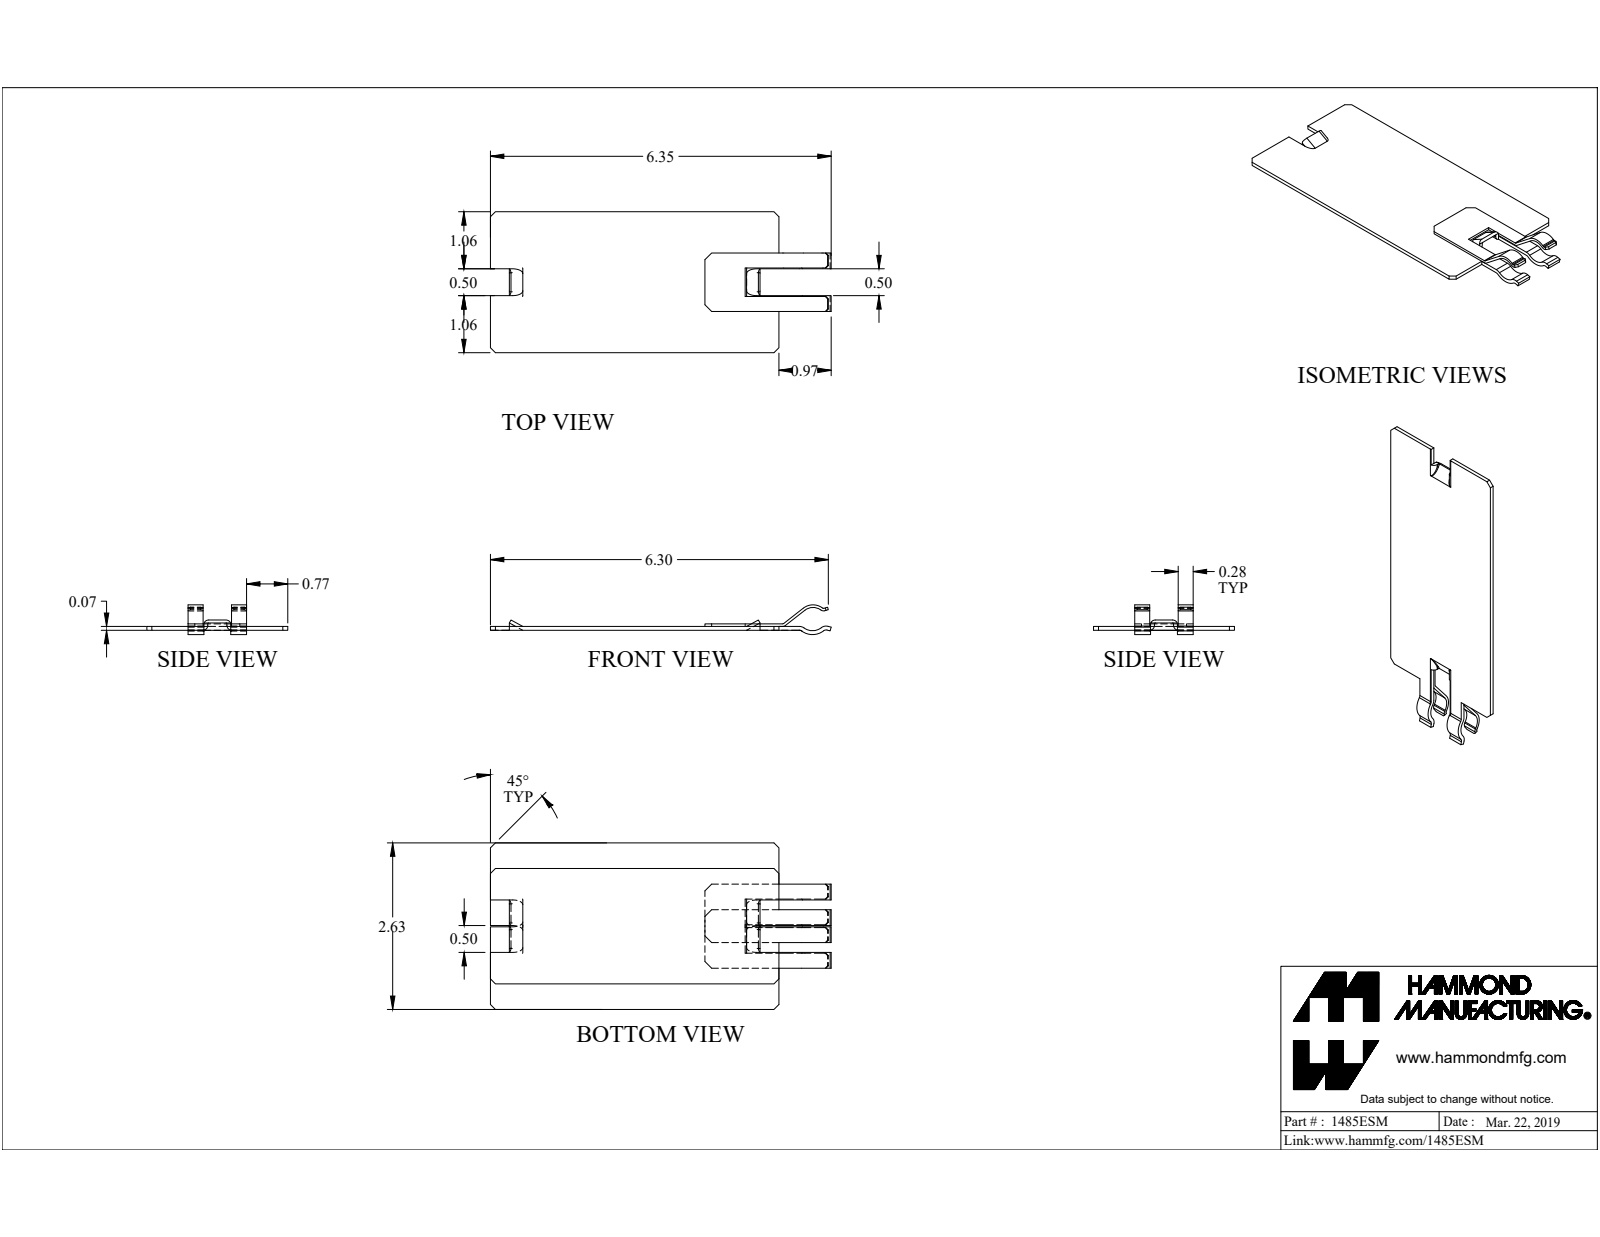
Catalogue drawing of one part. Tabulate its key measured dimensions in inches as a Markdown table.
| quantity | value |
| --- | --- |
| part name | 1485ESM |
| STEP written by | SolidWorks 2019 (CONFIG_CONTROL_DESIGN) |
| units | inches |
| bodies | 4 solids, 125 faces (83 planar, 36 cylindrical, 6 other) |
| overall size | 8.348 × 2.625 × 0.599 |
| volume | 1.986 in³ |
| surface area | 54.6 in² |
| partial cylindrical surfaces (radius × count) | 0.09 × 6, 0.015 × 4, 0.072 × 3, 0.144 × 2, 0.024 × 1, 0.03 × 1, 0.078 × 1, 0.245 × 1 |
| main face-to-face distances | 0.072, 0.125, 0.197, 0.048, 0.245, 0.12, 2.625, 0.75, 6.543, 0.768 |
